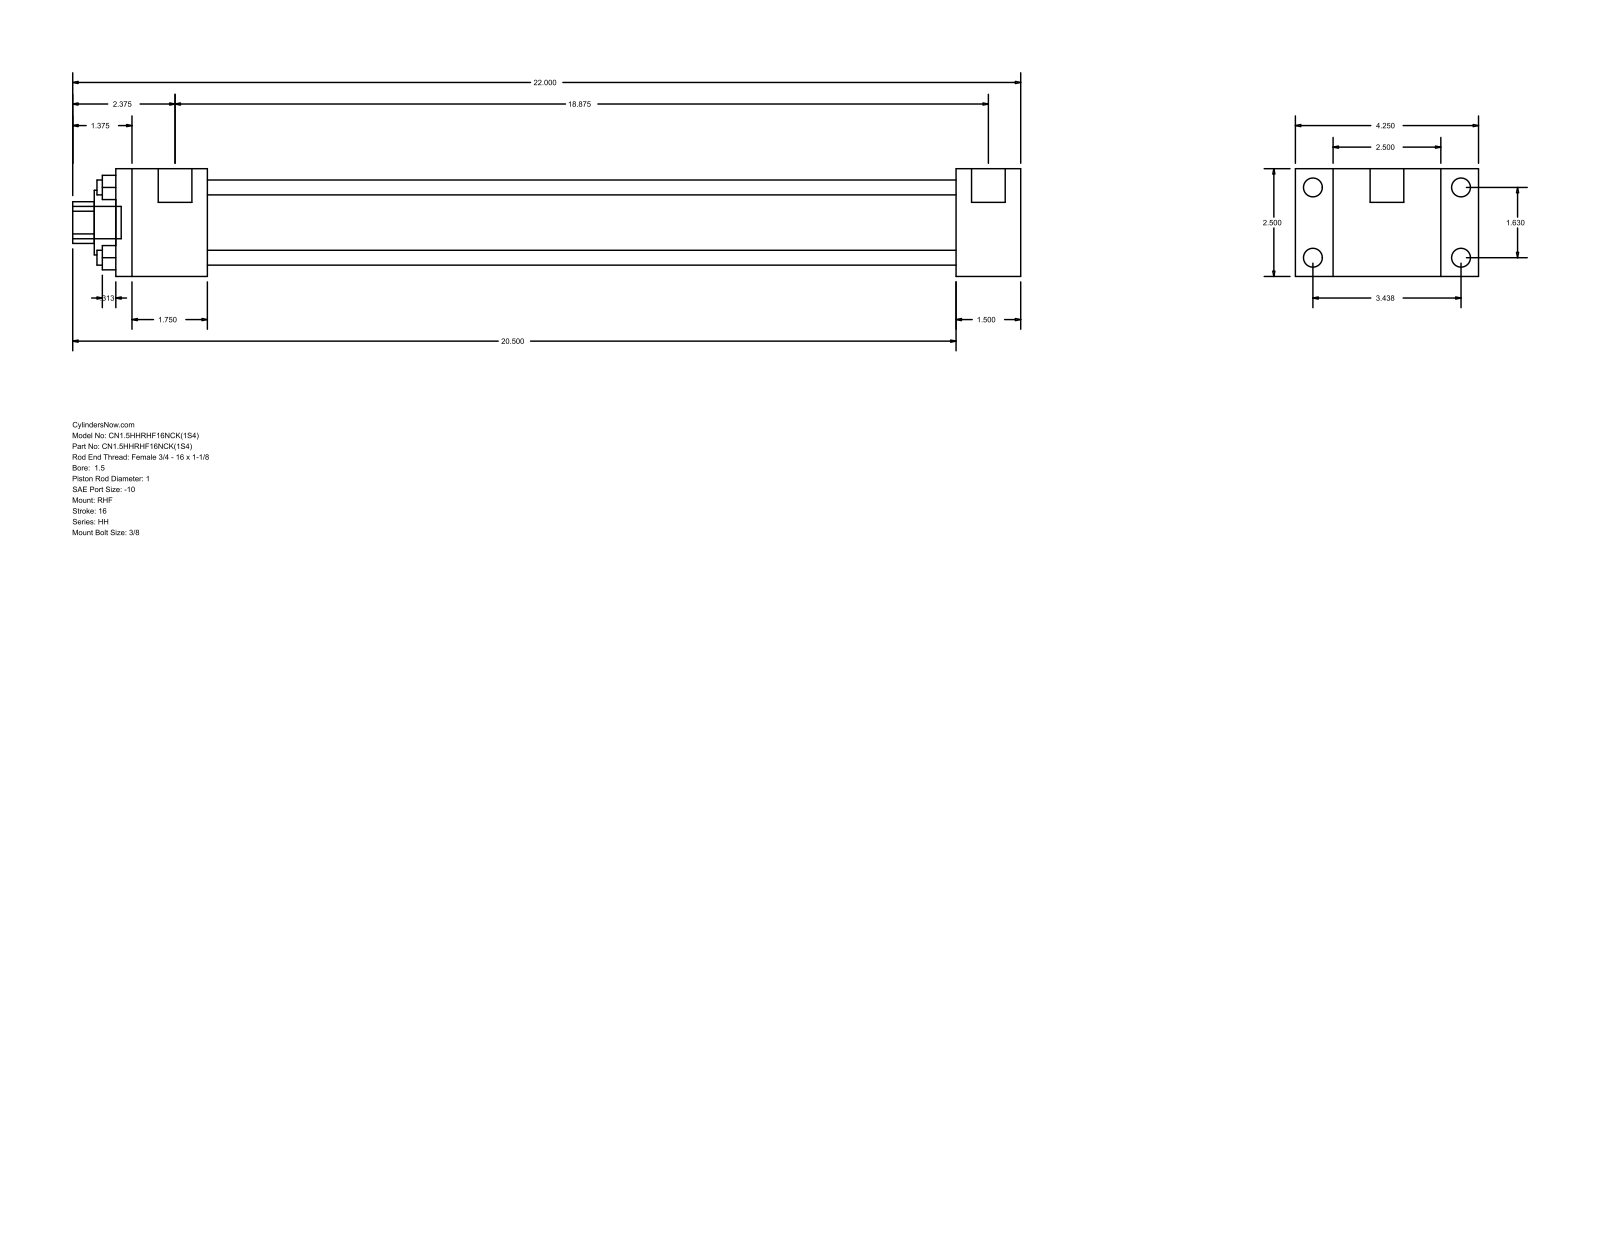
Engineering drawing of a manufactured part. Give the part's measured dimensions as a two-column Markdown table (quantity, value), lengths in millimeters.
| quantity | value |
| --- | --- |
| part name | HH_RHF__0150_1 |
| STEP written by | GSSL Pune (CONFIG_CONTROL_DESIGN) |
| units | millimeters |
| bodies | 0 solids, 88 faces (60 planar, 28 cylindrical, 0 other) |
| overall size | 558.8 × 107.95 × 63.5 |
| round holes (diameter × count) | 8.76 × 4, 25.4 × 1, 38.1 × 1, 44.45 × 1 |
| round bosses / shafts (diameter × count) | 11.13 × 4, 5.56 × 4, 19.84 × 2, 19.05 × 1 |
| partial cylindrical surfaces (radius × count) | 12.29 × 1 |
| main face-to-face distances | 63.5, 22.23, 85.73, 38.1, 107.96, 441.32, 479.42, 53.98, 495.3, 533.4 |
| hole center spacings | 29.27, 41.4, 58.55 |
